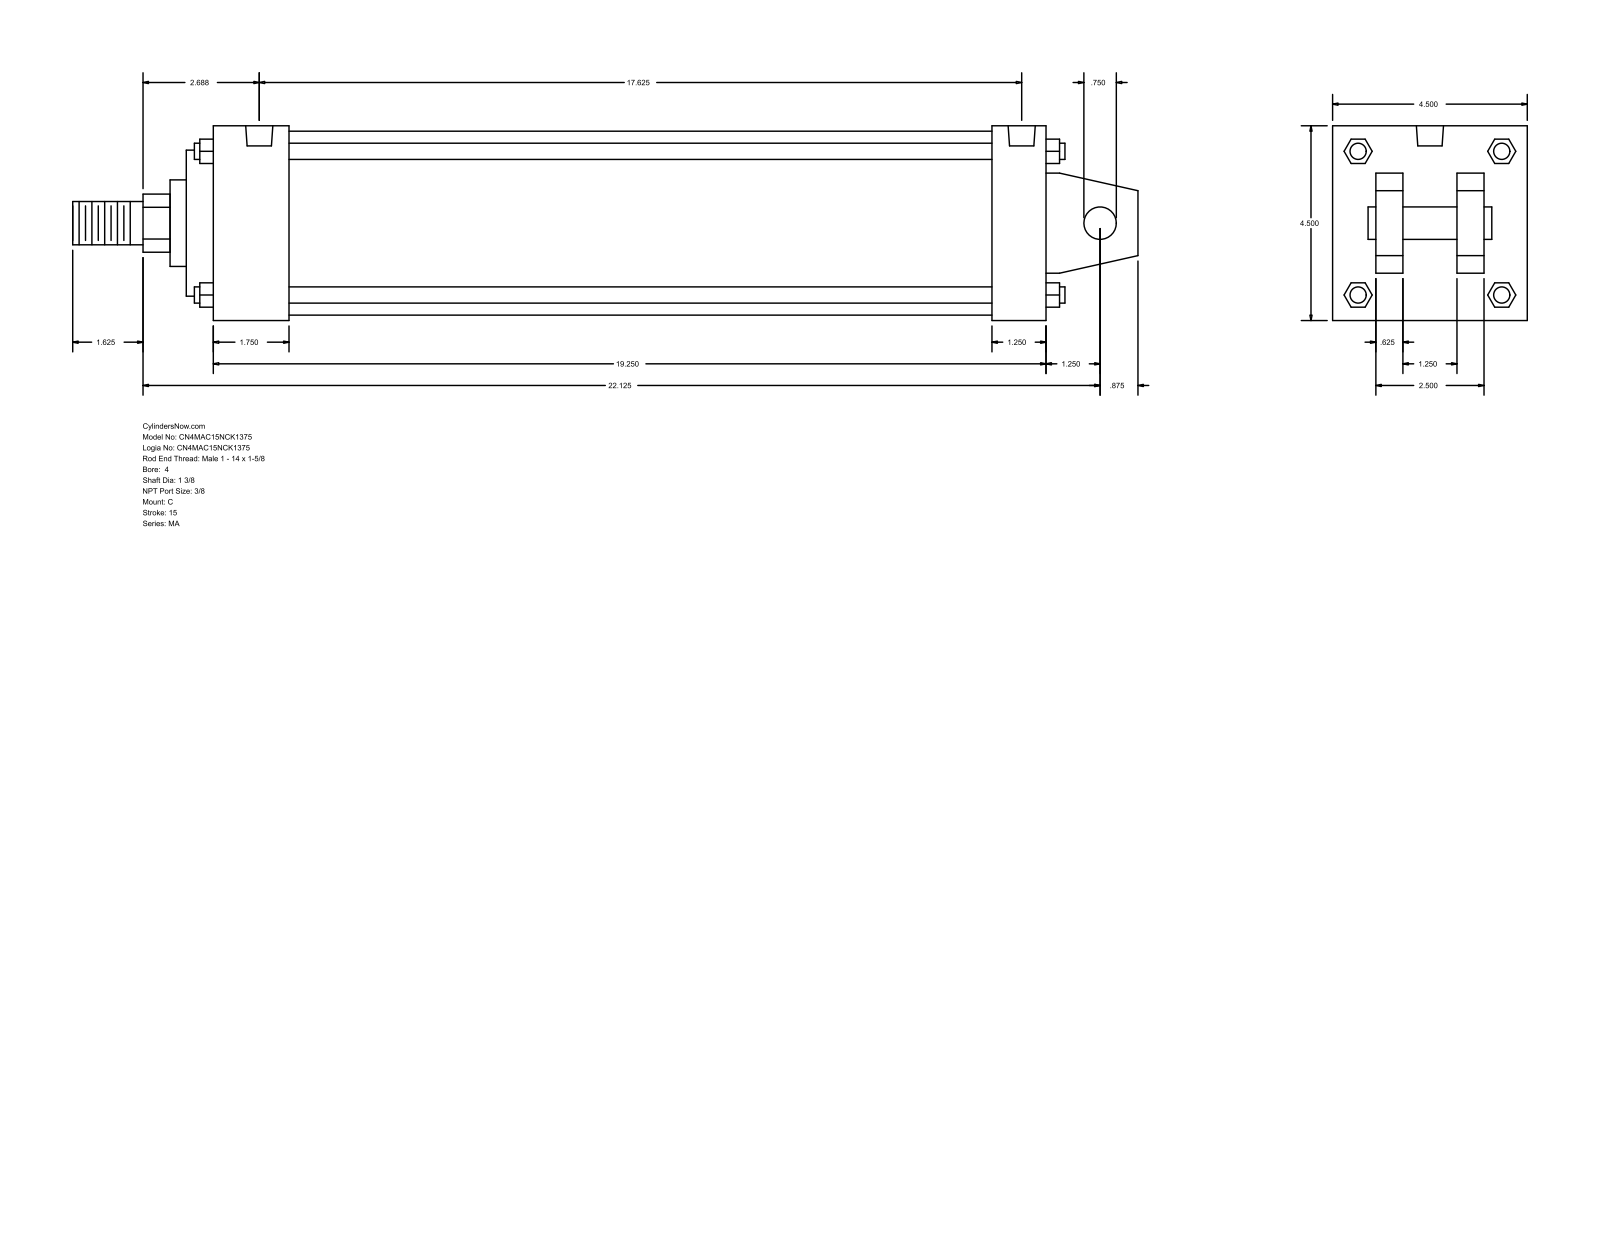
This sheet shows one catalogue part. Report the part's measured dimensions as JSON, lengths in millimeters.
{"part_name": "MA_C__0400_1.375", "step_written_by": "GSSL Pune (CONFIG_CONTROL_DESIGN)", "units": "millimeters", "bodies": {"solids": 0, "faces": 141, "planar": 109, "cylindrical": 32, "other": 0}, "overall_size": [625.48, 114.3, 114.3], "round_holes": [[11.11, 4], [15.93, 2]], "round_bosses_or_shafts": [[9.53, 4], [107.95, 1], [85.72, 1], [50.8, 1], [34.92, 1], [25.4, 1], [19.05, 1]], "partial_cylinders_radius": [[17.06, 1]], "face_to_face_distances": [114.3, 15.87, 488.96, 73.03, 41.27, 25.4, 88.9, 47.63, 504.83, 473.08], "hole_center_spacings": [438.15, 4.76, 4.77, 442.91, 442.92, 447.68]}
